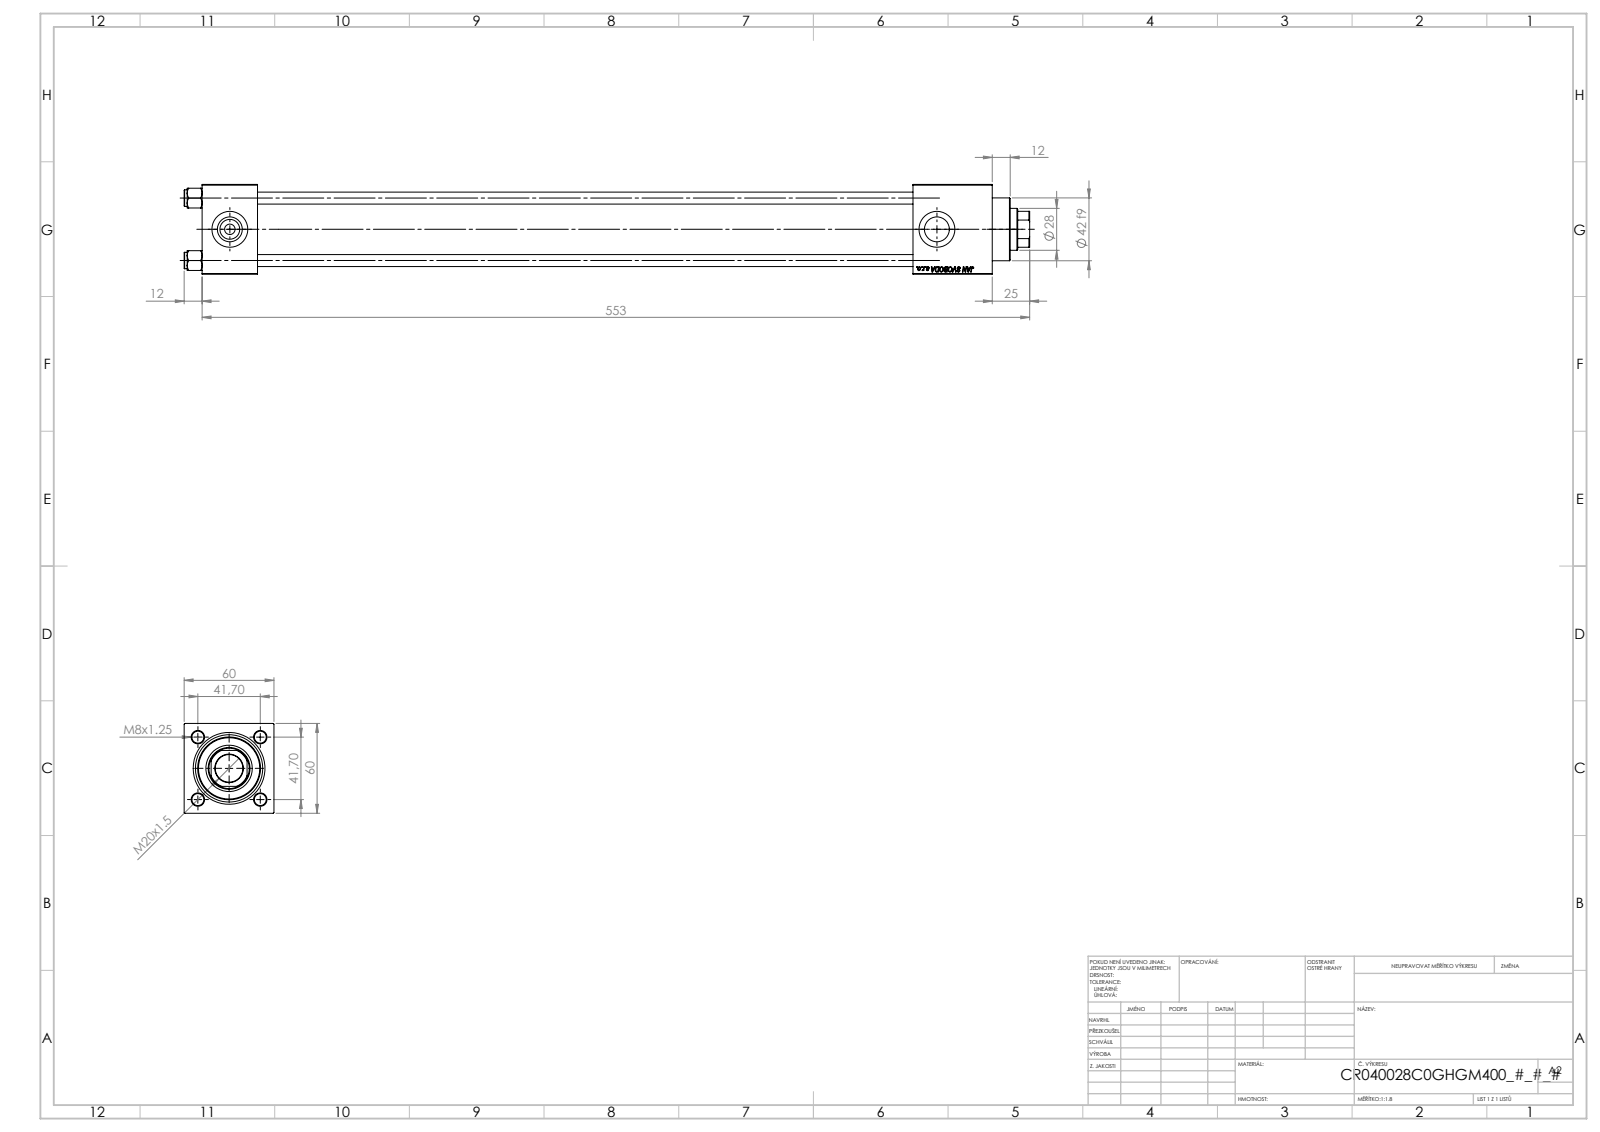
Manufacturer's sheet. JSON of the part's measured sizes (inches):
{"part_name": "V215_VC_A; V215CR_C_Body; V215CR_VCP_C; NUT_M5_C (+1 more)", "step_written_by": "SolidWorks 2019 (CONFIG_CONTROL_DESIGN)", "units": "inches", "bodies": {"solids": 11, "faces": 1148, "planar": 526, "cylindrical": 86, "other": 536}, "overall_size": [22.244, 2.362, 2.362], "volume_in3": 54.22, "surface_area_in2": 442.9, "round_holes": [[0.315, 4], [0.276, 2], [0.656, 2], [0.945, 2], [0.728, 1], [1.102, 1], [1.22, 1], [1.575, 1], [1.772, 1]], "round_bosses_or_shafts": [[0.433, 4], [1.811, 1], [1.654, 1]], "partial_cylinders_radius": [[0.531, 1]], "face_to_face_distances": [2.362, 1.457, 18.701, 17.244, 19.657, 18.201, 0.957, 2.087, 20.787, 19.331], "hole_center_spacings": [1.161, 1.642, 2.322, 18.602]}
